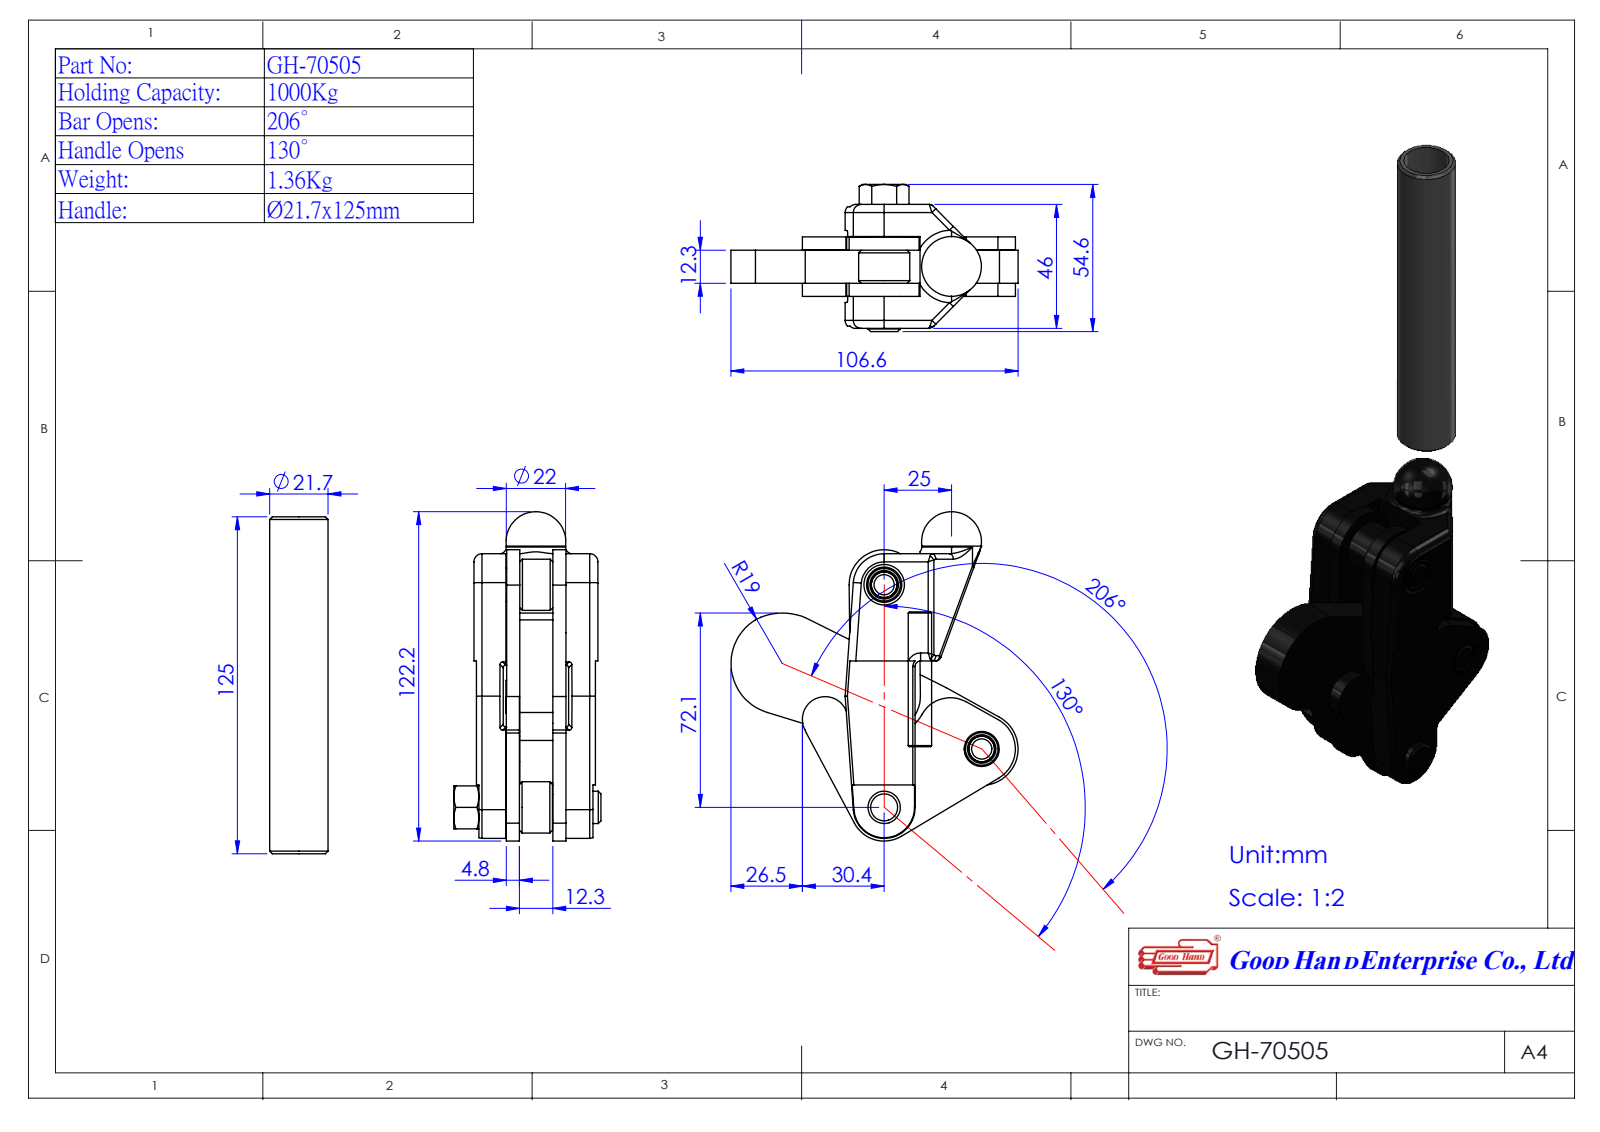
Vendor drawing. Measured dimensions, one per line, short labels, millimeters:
name: 3700808-1^GH-70505(簡化); Group5^GH-70505(簡化); Group3^GH-70505(簡化); Group1^GH-70505(簡化) (+2 more)
written by: SolidWorks 2016 (AUTOMOTIVE_DESIGN)
unit: mm
bodies: 5 solids, 158 faces (66 planar, 65 cylindrical, 27 other)
size: 246.8 × 106.08 × 54.6
volume: 189 747 mm³; area: 69 269 mm²
holes: 3× ⌀9.5, 1× ⌀10, 1× ⌀17.2
bosses: 1× ⌀21.96, 1× ⌀21.7, 1× ⌀19, 1× ⌀12, 1× ⌀9.5
rounds: 2× R2, 2× R11.5, 2× R12.5, 2× R13, 1× R8.43, 1× R11.1, 1× R12, 1× R13.5
face distances: 17.28, 4.85, 12.3, 17.15, 17.27, 4.97, 4.98, 22.25, 4.72, 12.43
hole spacings: 40.72, 41.1, 41.5, 42.2, 70.89, 82.6
